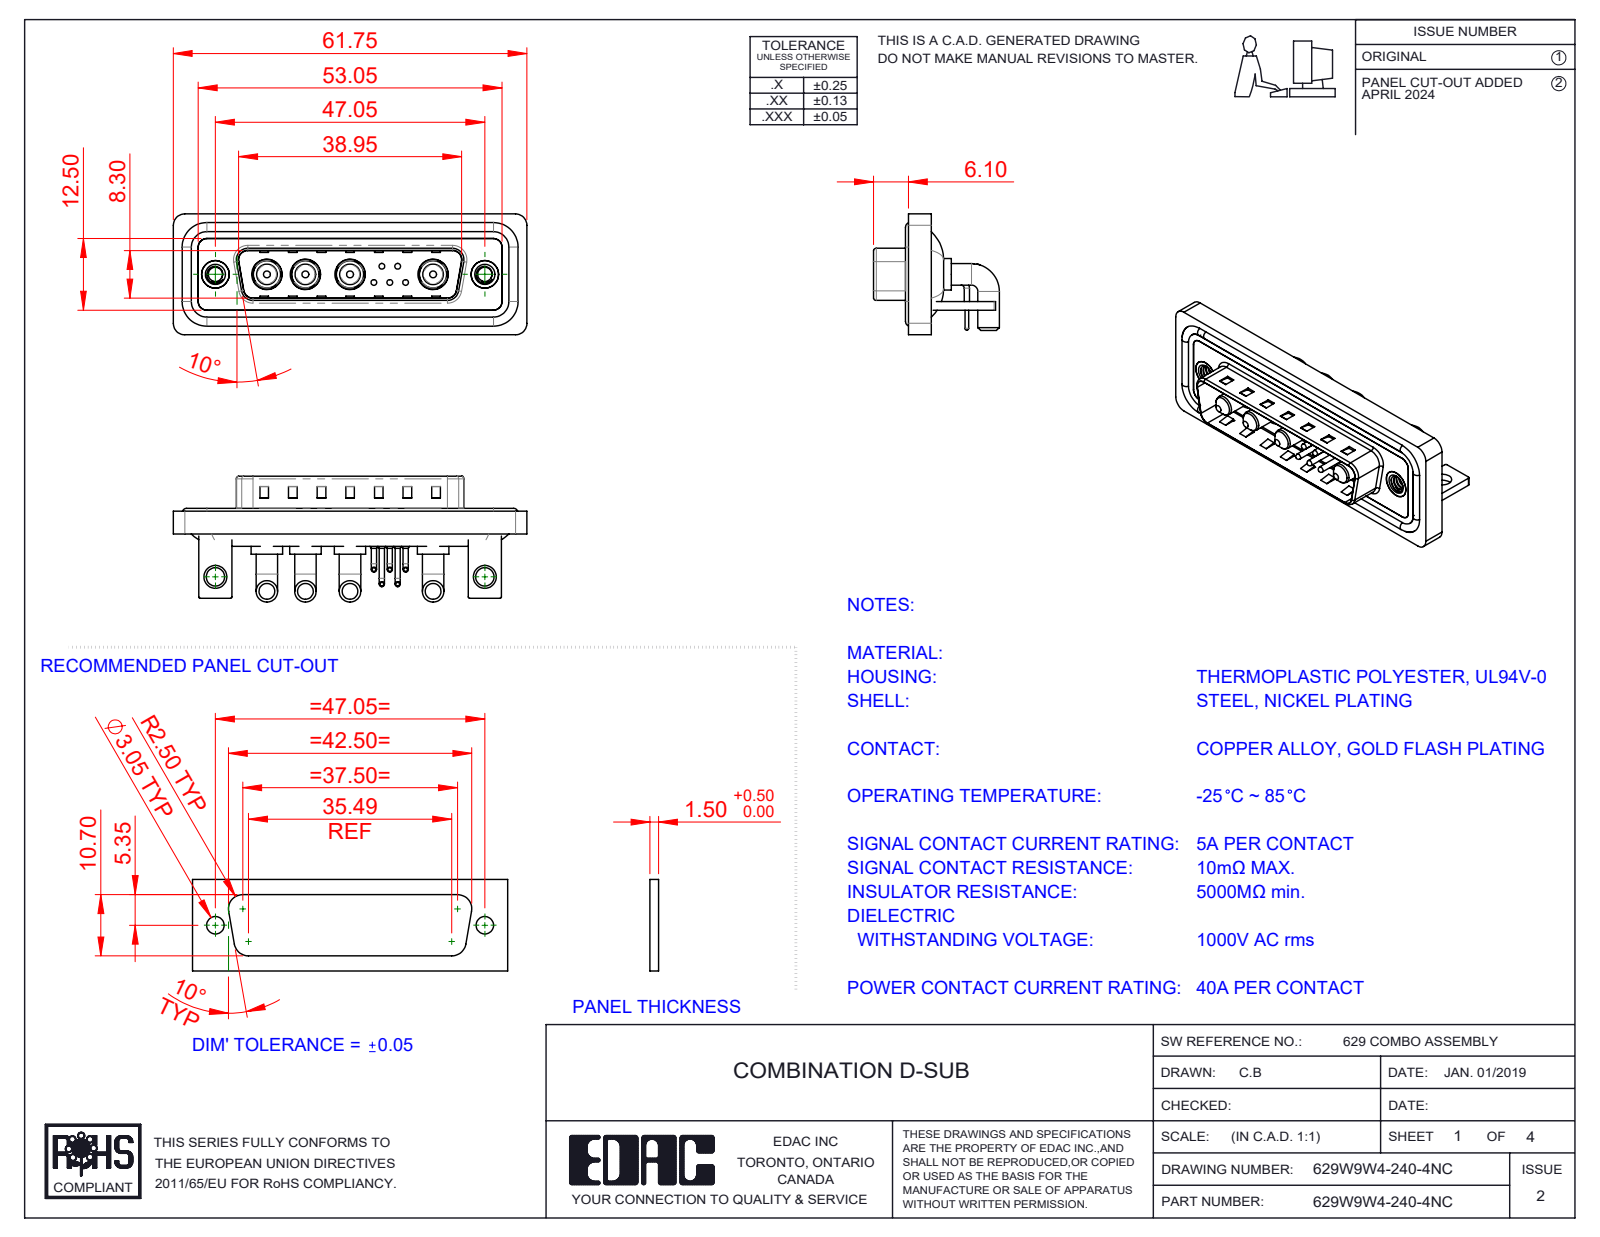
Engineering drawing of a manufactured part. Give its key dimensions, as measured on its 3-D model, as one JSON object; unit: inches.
{"part_name": "629Combo Shell Rear_25 Contacts; 629Combo Contact Row 1; 629Combo Threaded Rivet_B; Power Pin_40A RA (+6 more)", "step_written_by": "SolidWorks 2023 (CONFIG_CONTROL_DESIGN)", "units": "inches", "bodies": {"solids": 22, "faces": 1243, "planar": 589, "cylindrical": 470, "other": 184}, "overall_size": [2.431, 0.865, 0.831], "volume_in3": 0.505, "surface_area_in2": 20.37, "round_holes": [[0.03, 5], [0.063, 5], [0.079, 5], [0.191, 4], [0.209, 4], [0.098, 2], [0.126, 2], [0.157, 2], [0.189, 2], [0.197, 2]], "round_bosses_or_shafts": [[0.035, 10], [0.148, 8], [0.059, 5], [0.039, 5], [0.026, 5], [0.217, 4], [0.205, 4], [0.187, 4]], "partial_cylinders_radius": [[0.079, 19], [0.059, 18], [0.01, 16], [0.02, 9], [0.063, 8], [0.04, 5], [0.024, 4], [0.026, 4]], "face_to_face_distances": [0.016, 0.059, 0.031, 0.114, 0.083, 0.043, 0.146, 0.161, 0.177, 0.063], "hole_center_spacings": [0.124, 0.109, 0.198, 0.571, 1.852, 0.109, 0.173, 0.174]}
